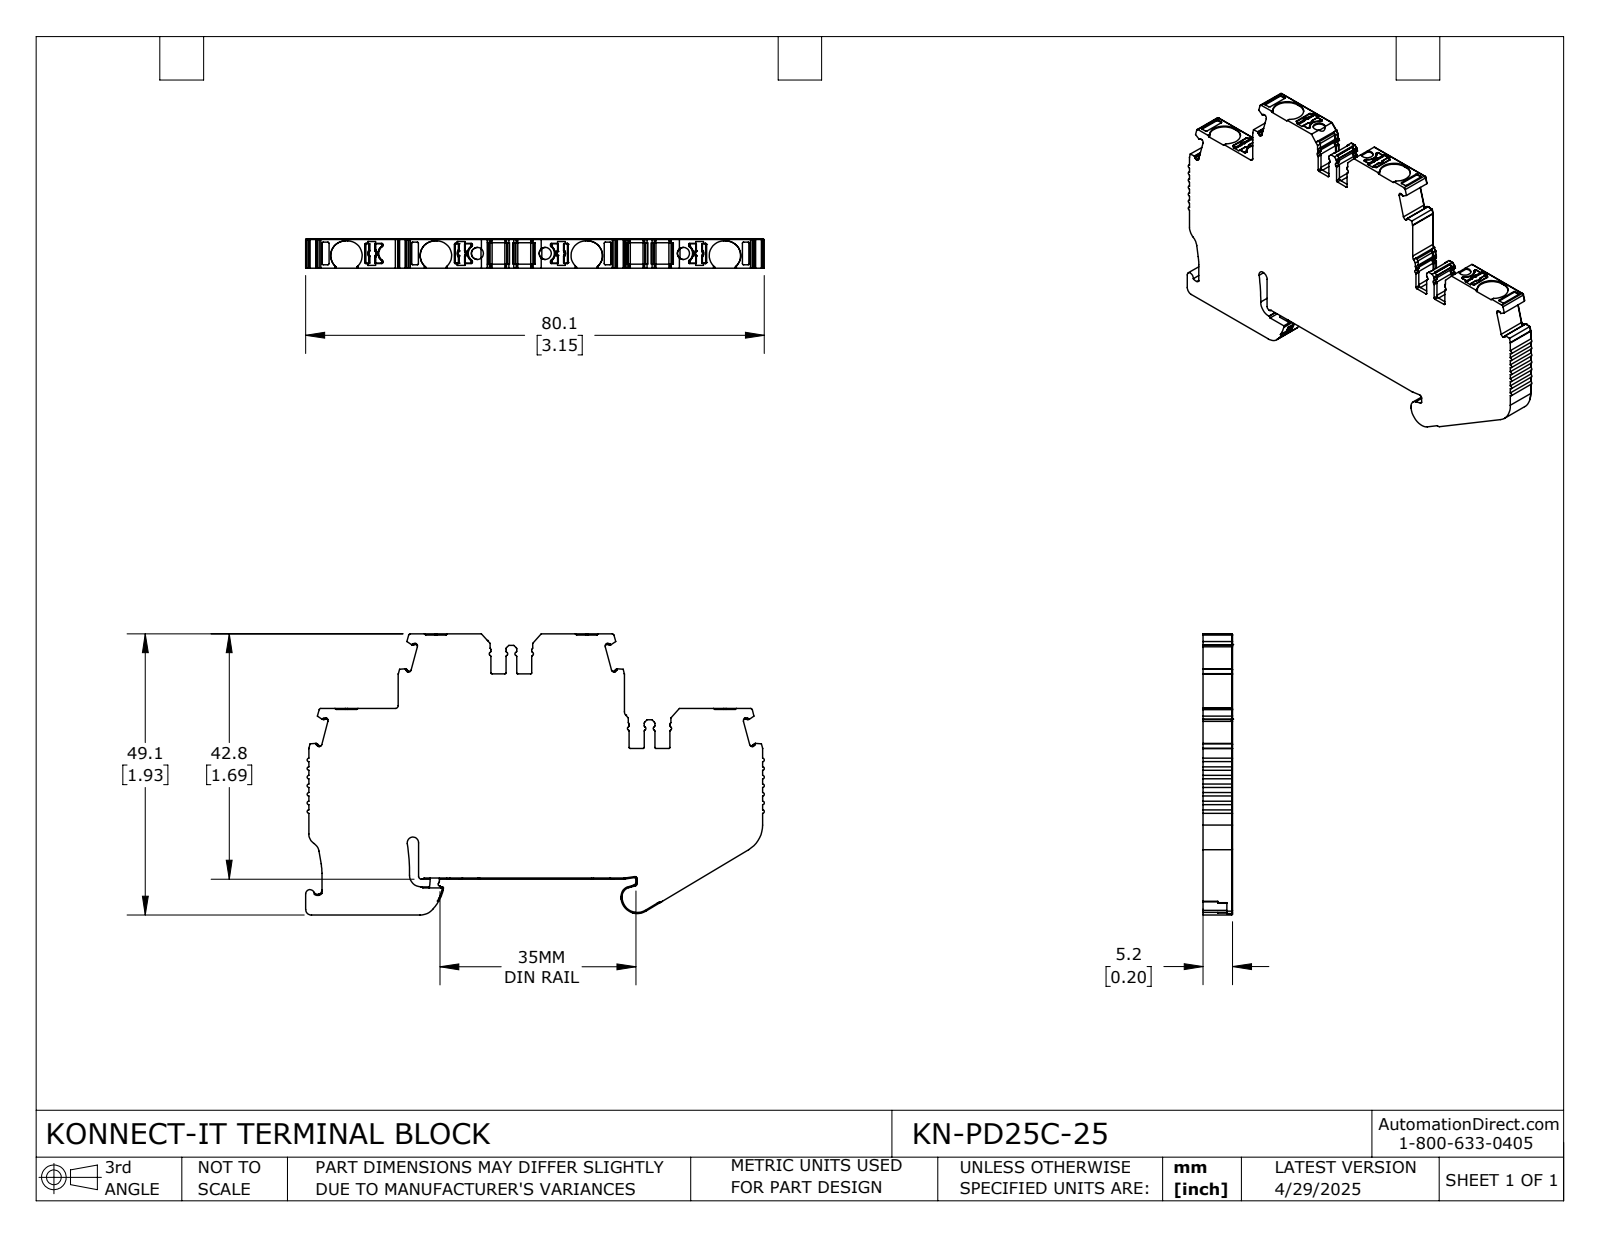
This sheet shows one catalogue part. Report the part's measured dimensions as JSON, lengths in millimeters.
{"part_name": "KN-PD25C-25", "step_written_by": "SolidWorks 2024 (CONFIG_CONTROL_DESIGN)", "units": "millimeters", "bodies": {"solids": 1, "faces": 1035, "planar": 503, "cylindrical": 463, "other": 69}, "overall_size": [80.09, 49.09, 5.15], "volume_mm3": 14524, "surface_area_mm2": 7555, "round_holes": [[2.1, 3]], "partial_cylinders_radius": [[0.2, 99], [0.3, 59], [0.1, 41], [0.4, 25], [0.5, 20], [0.15, 16], [0.6, 9], [1, 9]], "face_to_face_distances": [5.15, 13.01, 29.61, 42.62, 6.26, 48.88, 24.14, 35.87, 12.81, 6.46], "hole_center_spacings": [11.84, 24.14, 35.98]}
